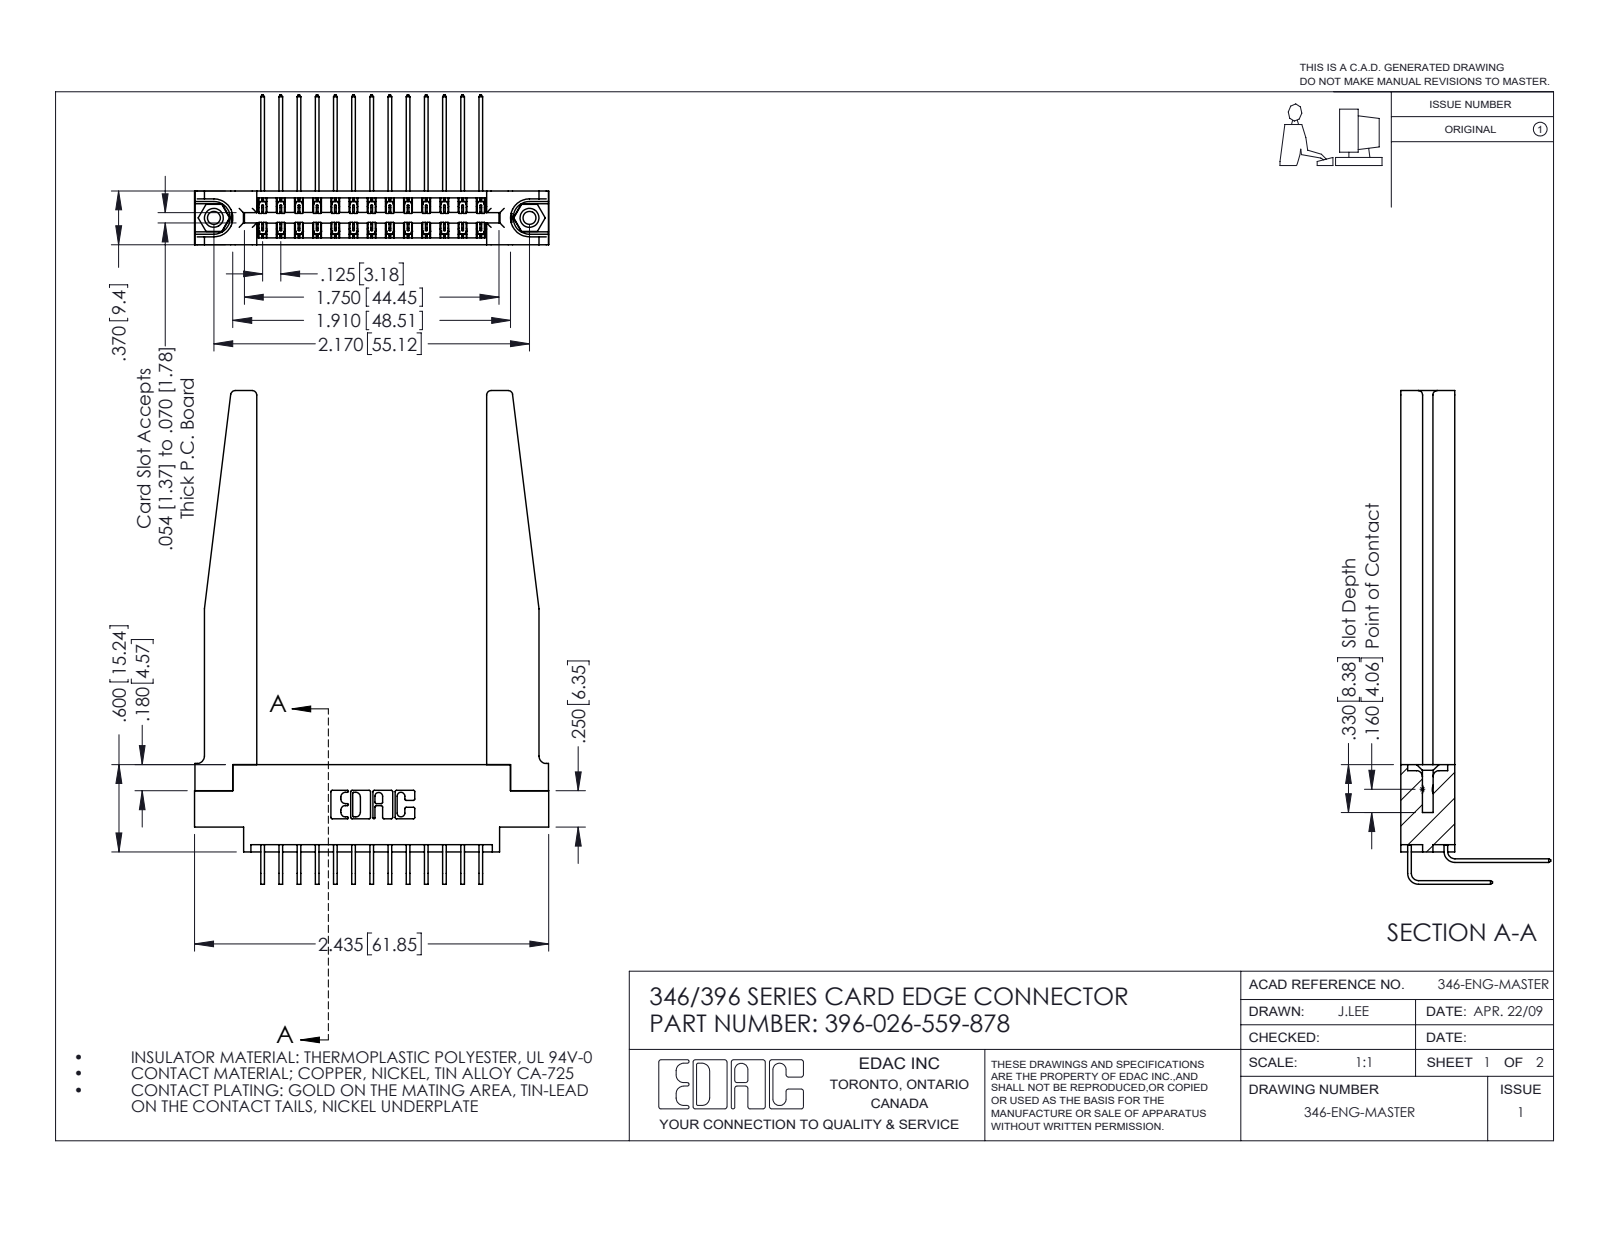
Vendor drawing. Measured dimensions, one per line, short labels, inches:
name: 345-250-001_345-250-001-102; 345-292-001_559 Tail - 2; 346 Part_0.170 Offset - 0.156 Dia-TH; 396-026-559-878 (+2 more)
written by: SolidWorks 2016 (CONFIG_CONTROL_DESIGN)
unit: in
bodies: 31 solids, 1764 faces (1184 planar, 528 cylindrical, 52 other)
size: 3.393 × 2.435 × 1.03
volume: 0.776 in³; area: 23.18 in²
holes: 2× ⌀0.089, 2× ⌀0.125, 2× ⌀0.156, 1× ⌀0.064
bosses: 2× ⌀0.155
rounds: 39× R0.006, 22× R0.01, 8× R0.03, 6× R0.007, 6× R0.031, 4× R0.05, 3× R0.026, 2× R0.014
face distances: 0.37, 0.15, 0.072, 0.048, 0.148, 0.322, 0.025, 0.25, 0.22, 0.102
hole spacings: 0.246, 1.964, 2.17
